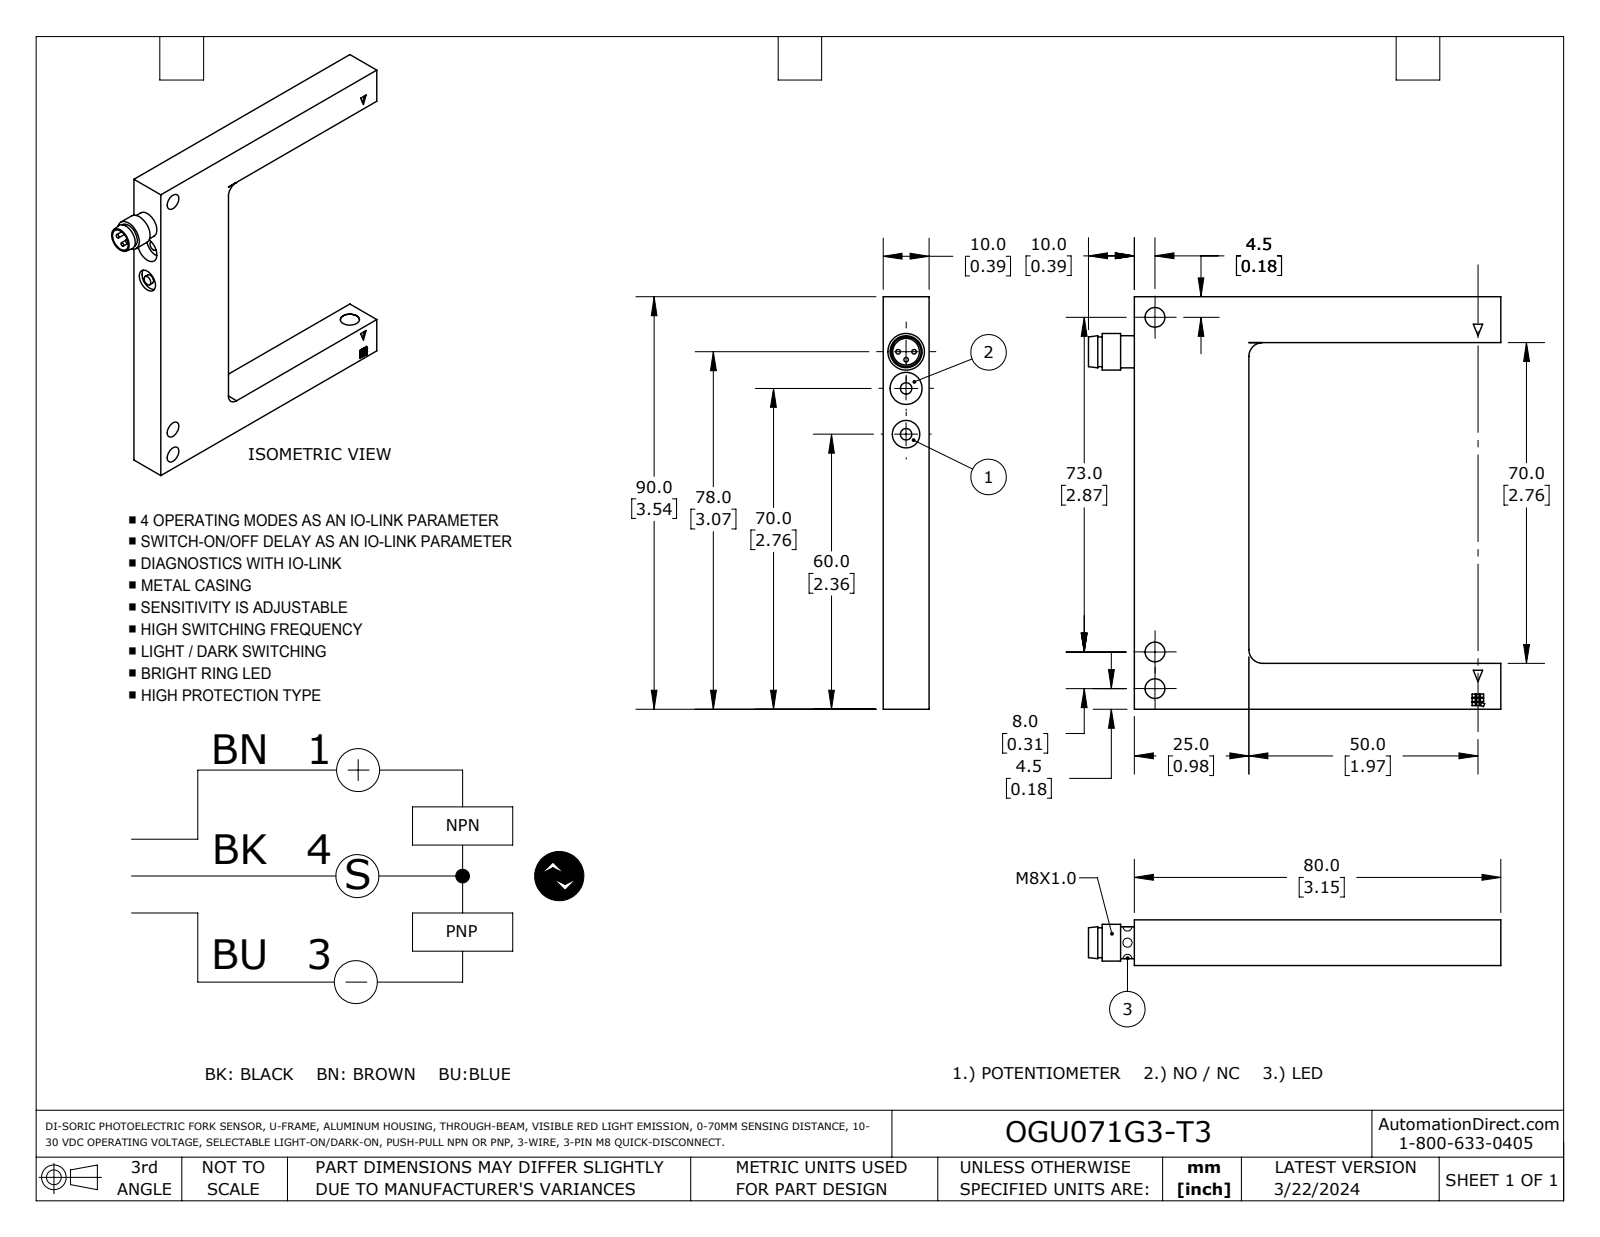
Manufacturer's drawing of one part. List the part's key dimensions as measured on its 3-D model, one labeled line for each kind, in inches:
Part name (STEP PRODUCT): OGU071G3-T3
STEP written by: SolidWorks 2023 (AUTOMOTIVE_DESIGN)
Units: inches
Bodies: 1 solid, 112 faces (91 planar, 20 cylindrical, 1 other)
Overall size (bounding box): 3.543 × 3.543 × 0.394
Volume: 2.029 in³ · Surface area: 18.69 in²
Round holes (diameter × count): ⌀0.169 ×3, ⌀0.118 ×1, ⌀0.197 ×1, ⌀0.228 ×1, ⌀0.236 ×1, ⌀0.276 ×1
Round bosses / shafts (diameter × count): ⌀0.039 ×3, ⌀0.098 ×2, ⌀0.315 ×1, ⌀0.276 ×1, ⌀0.256 ×1
Partial cylindrical surfaces — rounded edges, fillets, slot ends (radius × count): R0.118 ×3
Main face-to-face distances: 0.394, 3.15, 3.543, 0.984, 2.756, 2.165, 0.392, 0.039, 3.152, 2.758
Hole centre spacings: 0.315, 0.394, 0.709, 2.874, 3.189
